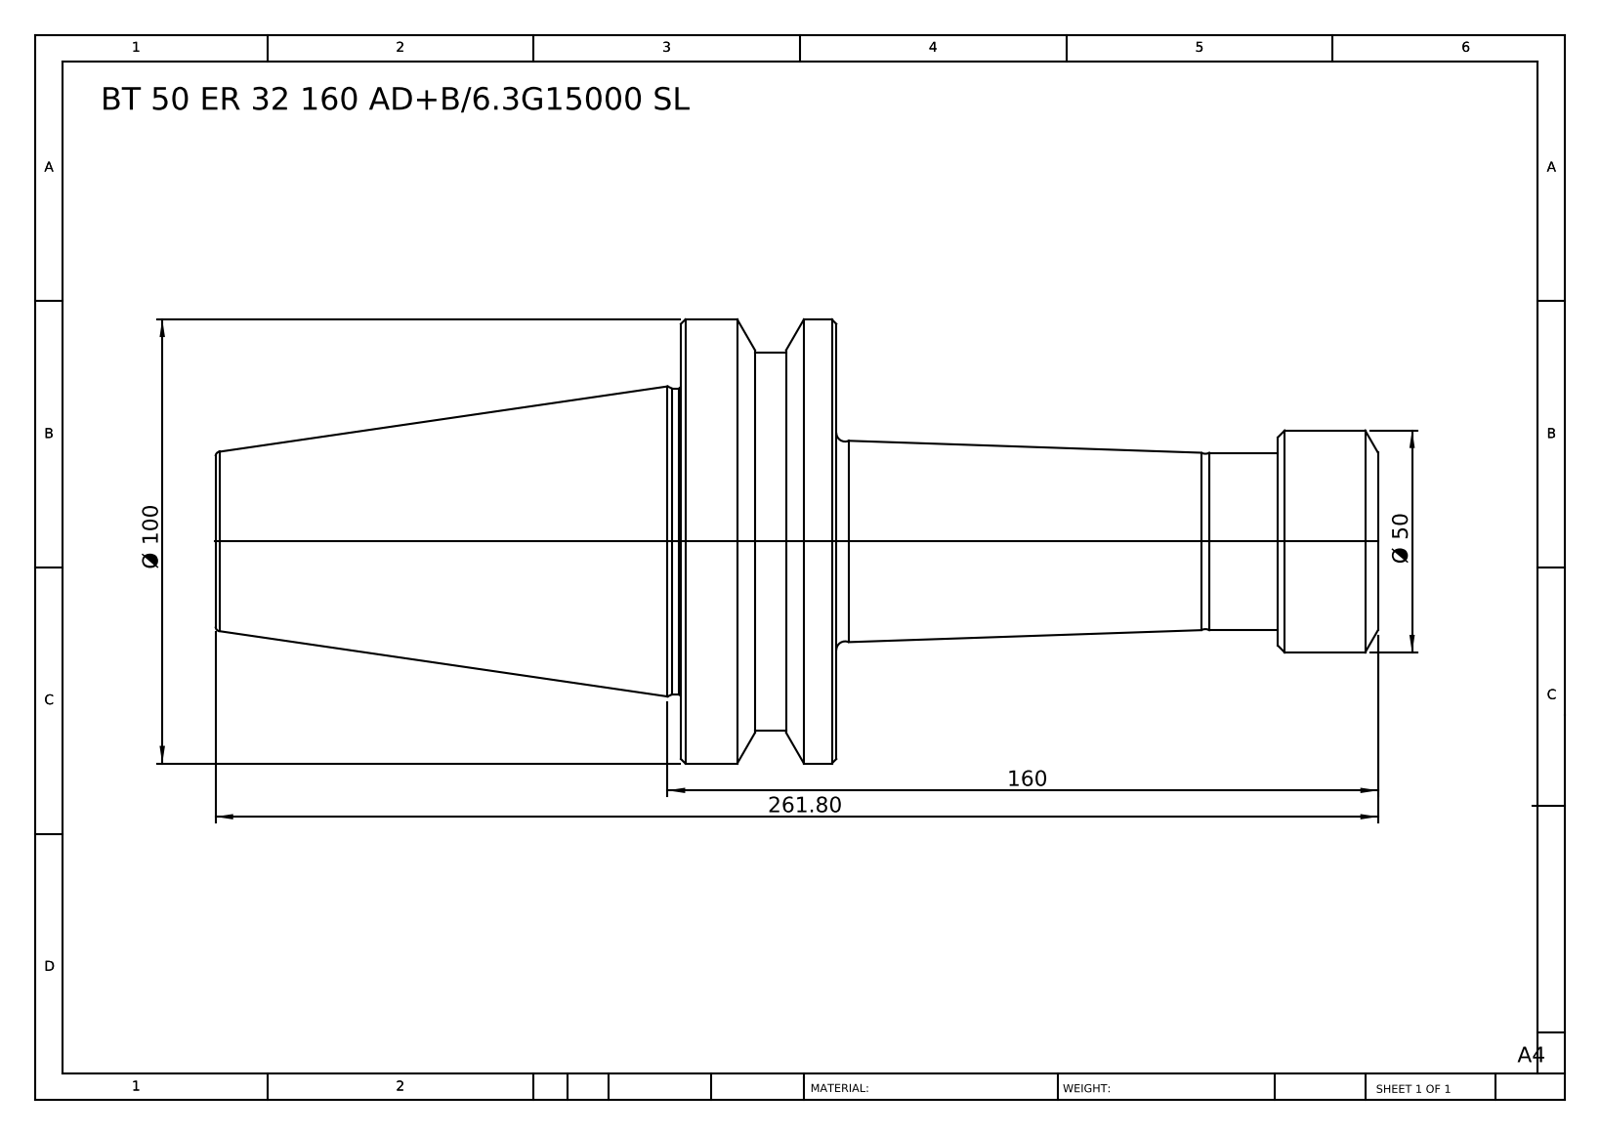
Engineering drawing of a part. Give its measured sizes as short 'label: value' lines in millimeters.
name: BT 50 ER 32 160 AD-6.3G15000 SL
written by: SolidWorks 2014 (CONFIG_CONTROL_DESIGN)
unit: mm
bodies: 1 solid, 51 faces (7 planar, 12 cylindrical, 32 other)
size: 261.8 × 100 × 100
volume: 692 772 mm³; area: 61 604 mm²
bosses: 1× ⌀100, 1× ⌀85, 1× ⌀69, 1× ⌀50, 1× ⌀39.9
face distances: 35, 122, 157, 261.8, 139.8, 104.8, 22.5, 99.5, 134.5, 239.3
